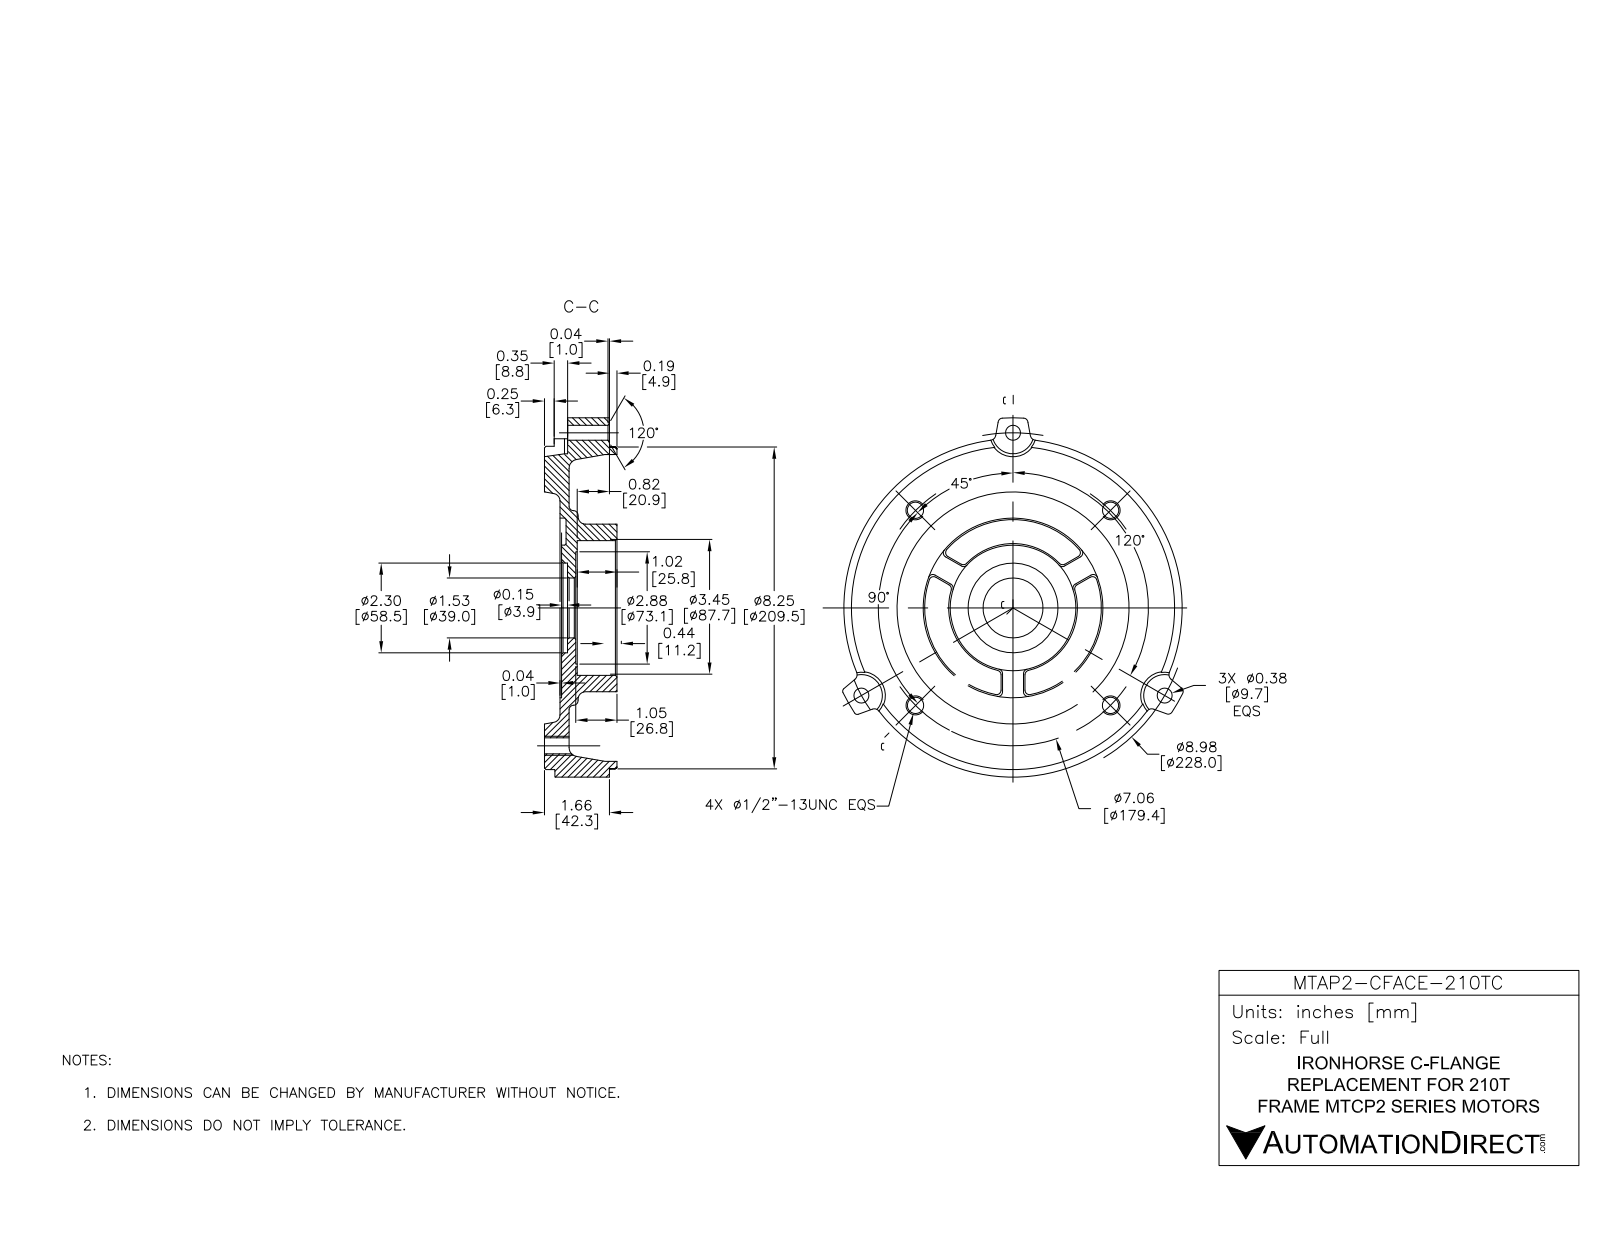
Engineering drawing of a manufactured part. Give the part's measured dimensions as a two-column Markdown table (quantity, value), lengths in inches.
| quantity | value |
| --- | --- |
| part name | MTAP2-CFACE-210TC |
| STEP written by | SolidWorks 2017 (AUTOMOTIVE_DESIGN) |
| units | inches |
| bodies | 1 solid, 131 faces (32 planar, 67 cylindrical, 32 other) |
| overall size | 9.409 × 9.027 × 1.902 |
| volume | 47.34 in³ |
| surface area | 245.6 in² |
| round holes (diameter × count) | 0.472 × 4, 0.394 × 3, 1.575 × 1, 2.362 × 1, 2.953 × 1, 3.543 × 1, 4.646 × 1, 4.724 × 1 |
| round bosses / shafts (diameter × count) | 8.819 × 1, 8.5 × 1, 8.465 × 1, 4.173 × 1, 3.386 × 1, 3.307 × 1 |
| partial cylindrical surfaces (radius × count) | 0.039 × 12, 0.571 × 3, 5 × 1 |
| main face-to-face distances | 0.642, 0.236, 0.256, 0.406, 0.563, 0.039, 0.157, 0.413, 0.079, 1.709 |
| hole center spacings | 4.606, 7.978, 3.278, 3.625, 3.625, 5.126, 5.127, 7.25 |
